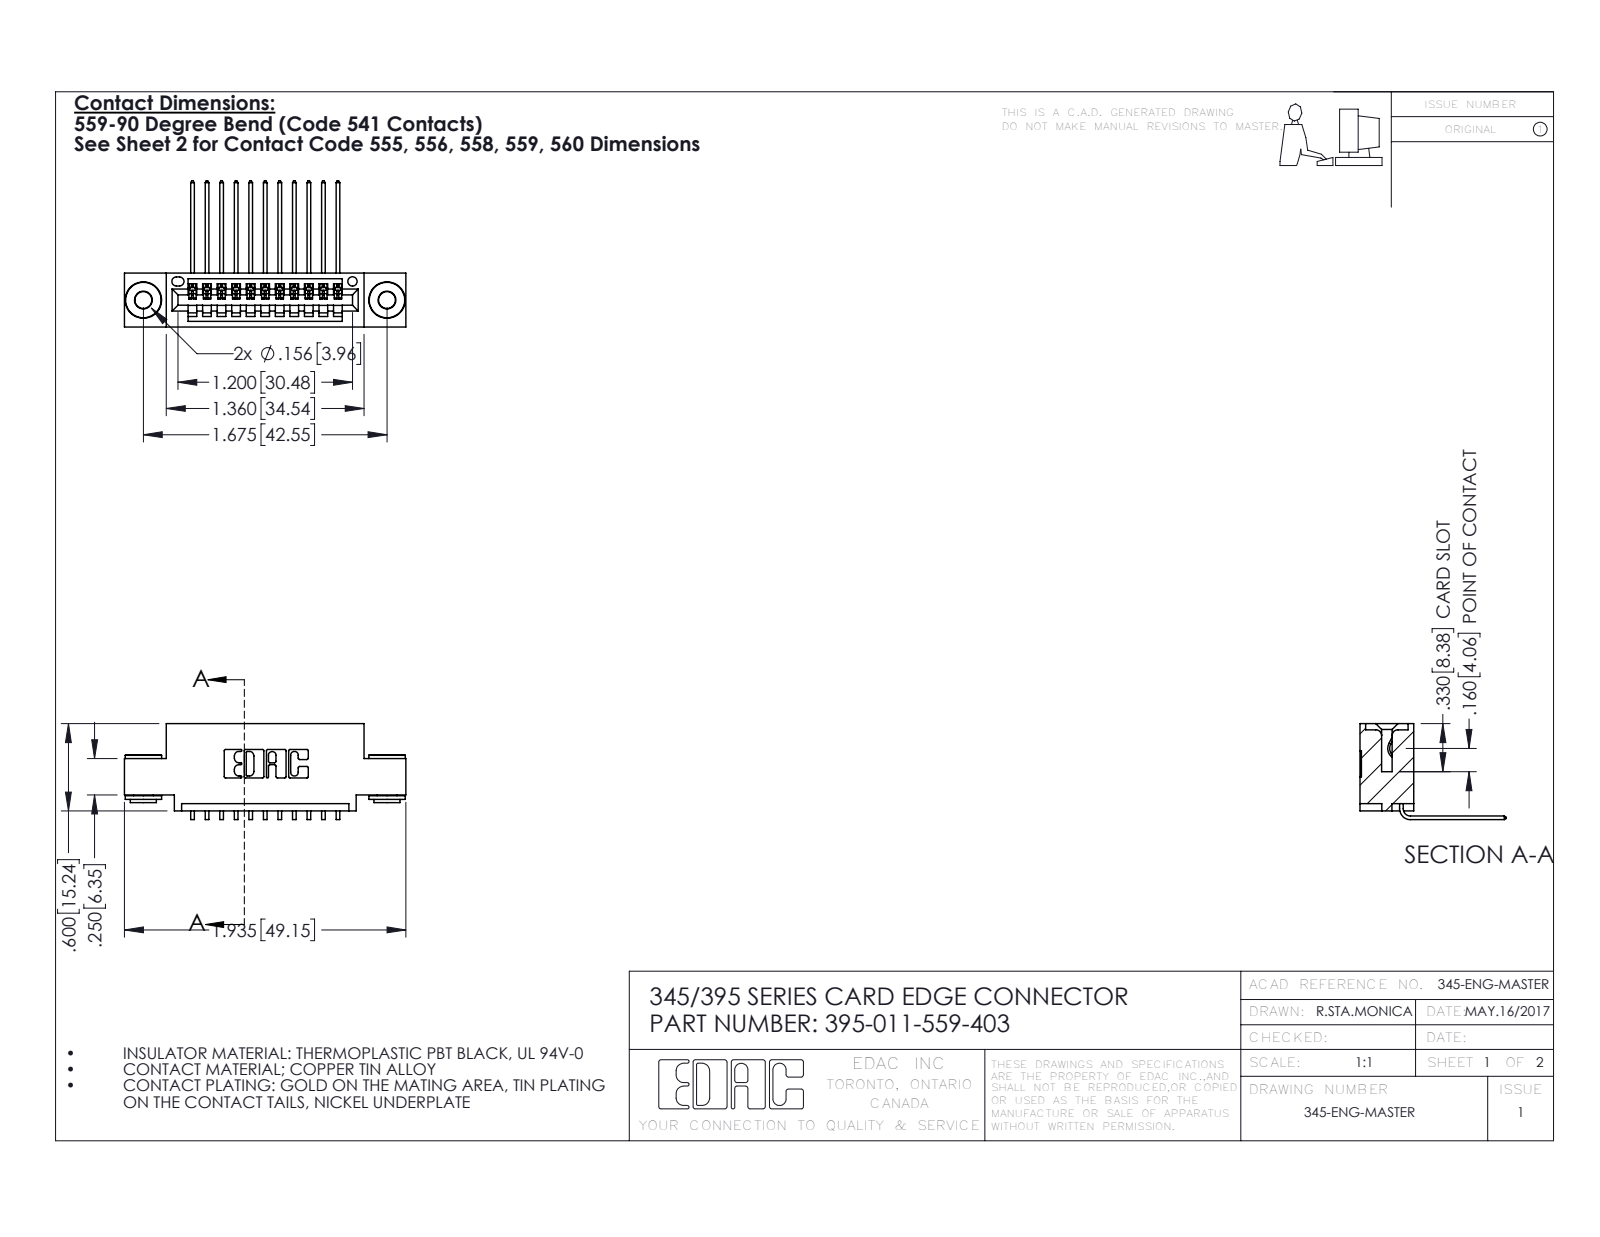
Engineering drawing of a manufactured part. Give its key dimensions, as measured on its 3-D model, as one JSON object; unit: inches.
{"part_name": "345-250-002_345-250-002-102; 345-292-001_558 559 Tail - 1; 395-011-559-403; 345 Part_0.110 Offset - 0.156 Dia-TH", "step_written_by": "SolidWorks 2016 (CONFIG_CONTROL_DESIGN)", "units": "inches", "bodies": {"solids": 14, "faces": 828, "planar": 556, "cylindrical": 264, "other": 8}, "overall_size": [1.935, 1.005, 0.659], "volume_in3": 0.268, "surface_area_in2": 9.197, "round_holes": [[0.116, 2], [0.156, 2], [0.064, 1]], "round_bosses_or_shafts": [[0.25, 2], [0.18, 2], [0.136, 2]], "partial_cylinders_radius": [[0.006, 22], [0.01, 22], [0.007, 6], [0.031, 6], [0.026, 3], [0.031, 2], [0.04, 2], [0.014, 1]], "face_to_face_distances": [0.2, 0.072, 0.298, 0.37, 0.025, 0.098, 0.272, 0.1, 0.6, 0.06], "hole_center_spacings": [0.27, 1.443, 1.675]}
